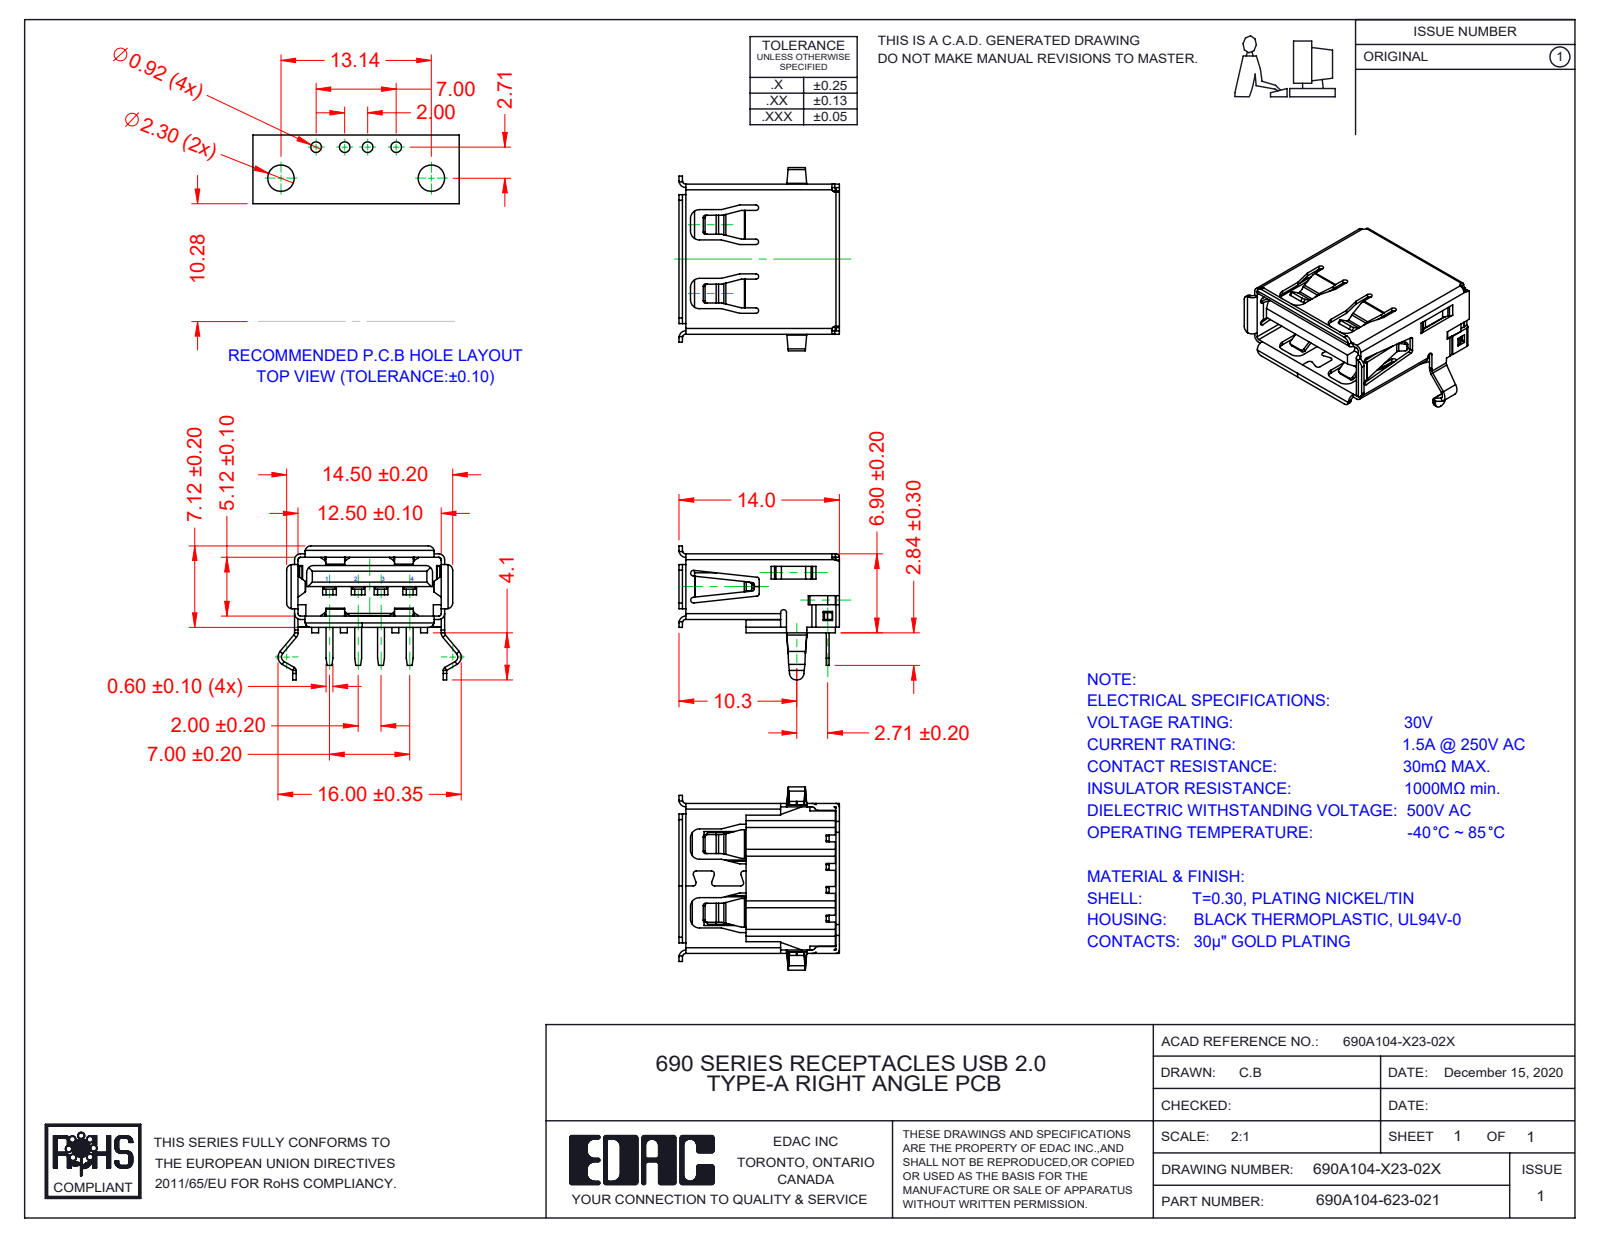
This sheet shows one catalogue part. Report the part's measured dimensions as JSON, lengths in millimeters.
{"part_name": "Insulator 690A104-X23-02X_Black; Shell 690A104-X23-02X; Contact 690A104-X23-02X; 690A104-123-021", "step_written_by": "SolidWorks 2020 (AUTOMOTIVE_DESIGN)", "units": "millimeters", "bodies": {"solids": 6, "faces": 869, "planar": 656, "cylindrical": 187, "other": 26}, "overall_size": [16, 14, 11.7], "volume_mm3": 576, "surface_area_mm2": 2131, "partial_cylinders_radius": [[0.2, 30], [0.5, 24], [0.3, 18], [0.6, 12], [0.25, 10], [0.1, 8], [0.8, 8], [0.24, 4]], "face_to_face_distances": [5.42, 5.12, 12.8, 1.01, 1.56, 1.26, 0.55, 0.71, 4.41, 4.16]}
